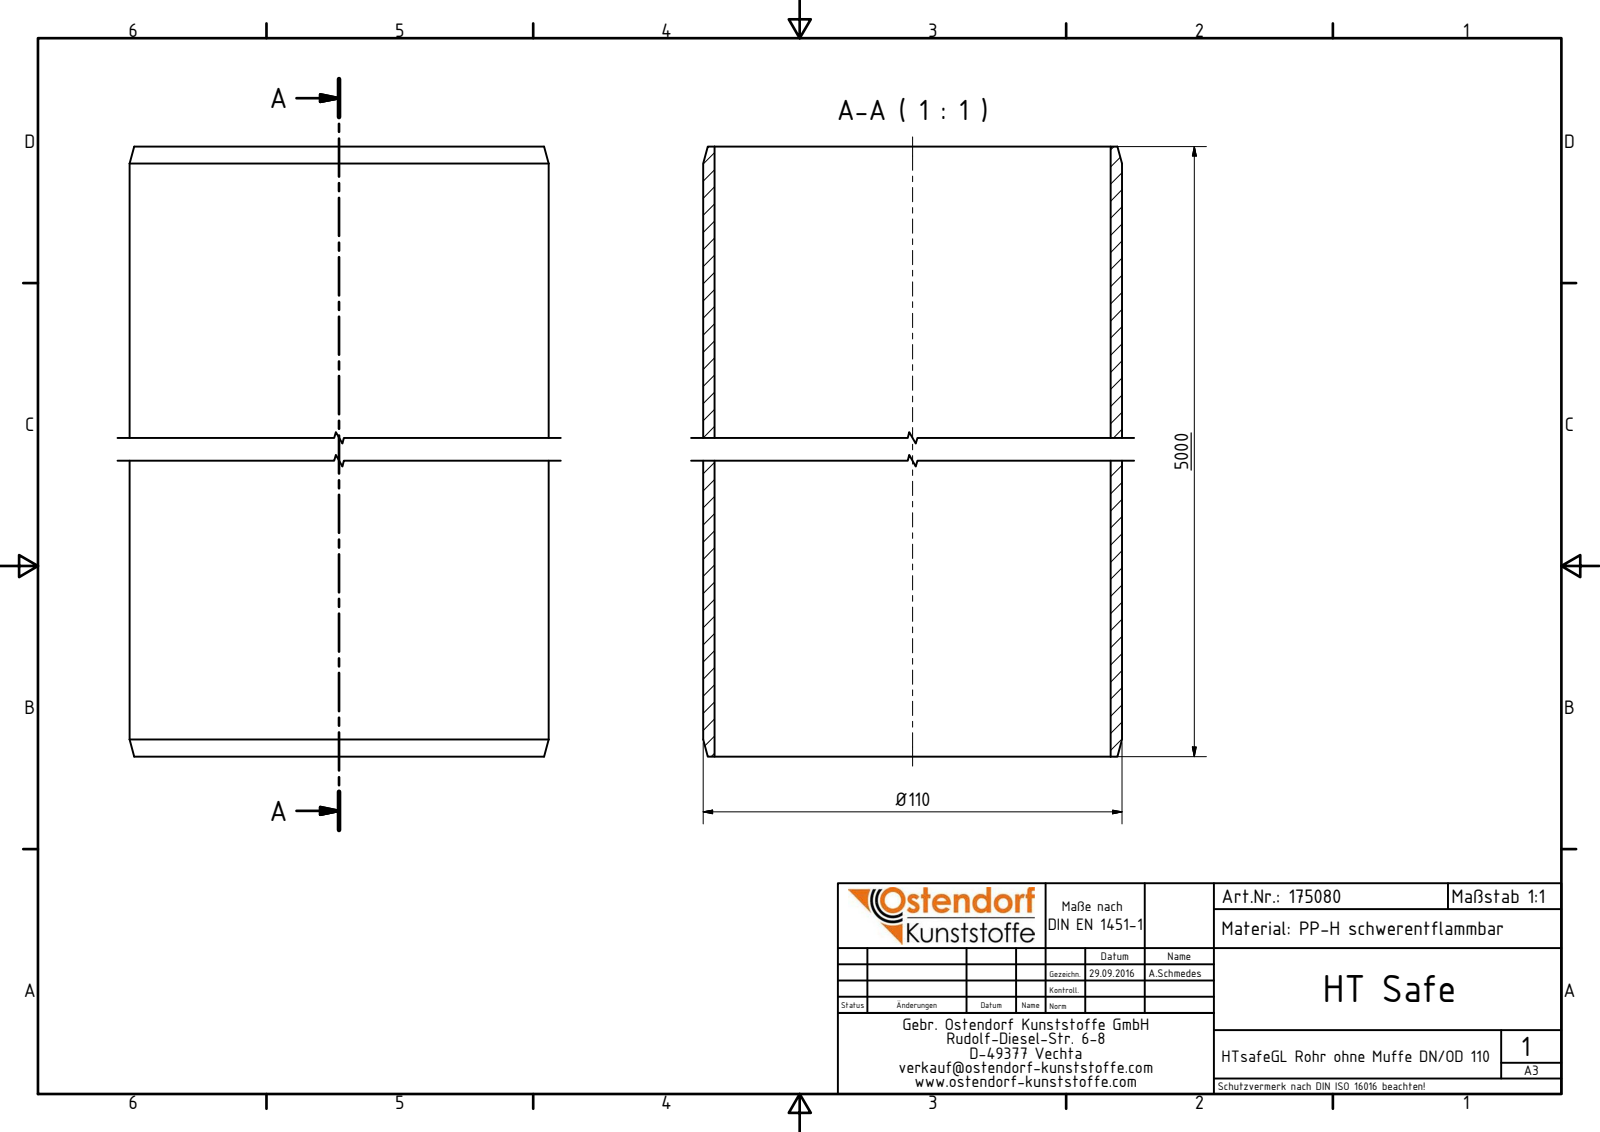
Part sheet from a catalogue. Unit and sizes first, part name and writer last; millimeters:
Units: millimetres
Overall size (bounding box): 5000 × 110 × 110
Round holes (diameter × count): ⌀104 ×1
Round bosses / shafts (diameter × count): ⌀110 ×1
Main face-to-face distances: 5000
Volume: 5 040 000 mm³ · Surface area: 3 363 000 mm²
Bodies: 1 solid, 6 faces (2 planar, 2 cylindrical, 2 other)
Part name (STEP PRODUCT): 175080 HTsafeGL DN_OD 110x5000
STEP written by: Autodesk Inventor 2016 (AUTOMOTIVE_DESIGN)
